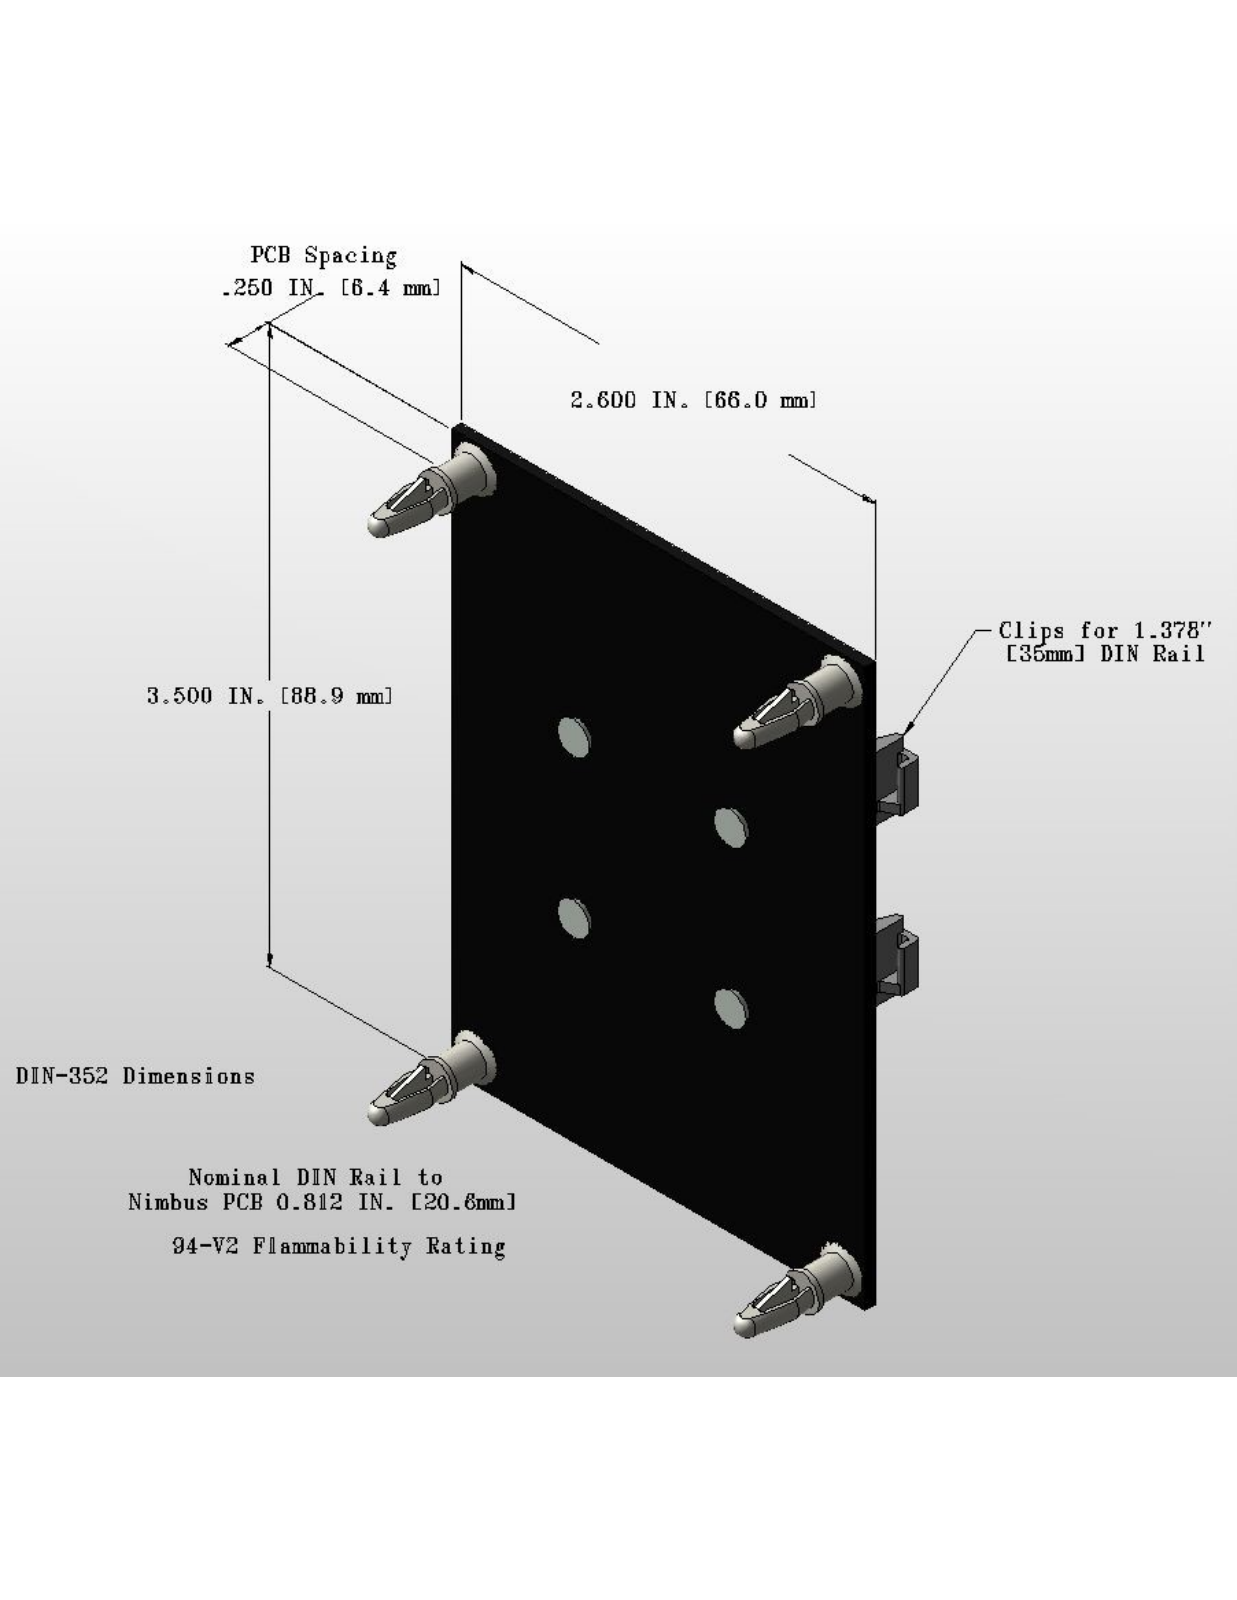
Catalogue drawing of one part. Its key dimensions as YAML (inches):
step_written_by: "KeyCreator Pro (AP242_MANAGED_MODEL_BASED_3D_ENGINEERING_MIM_LF)"
units: inches
bodies: {solids: 11, faces: 536, planar: 310, cylindrical: 186, other: 40}
overall_size: [3.5, 2.6, 1.46]
volume: 0.96
surface_area: 34.15
round_holes:
  - {diameter: 0.156, count: 8}
  - {diameter: 0.108, count: 6}
  - {diameter: 0.079, count: 1}
  - {diameter: 0.118, count: 1}
round_bosses_or_shafts:
  - {diameter: 0.281, count: 4}
  - {diameter: 0.218, count: 4}
  - {diameter: 0.187, count: 4}
partial_cylinders:
  - {radius: 0.016, count: 20}
  - {radius: 0.039, count: 6}
  - {radius: 0.128, count: 6}
  - {radius: 0.02, count: 4}
  - {radius: 0.076, count: 4}
  - {radius: 0.079, count: 4}
  - {radius: 0.086, count: 4}
  - {radius: 0.02, count: 3}
face_to_face_distances: [0.062, 0.053, 0.984, 0.357, 0.295, 0.115, 0.242, 0.394, 0.984, 0.057]
hole_center_spacings: [0.984, 0.492, 1.1, 1.289, 1.597, 1.981, 2.193, 2.387]
